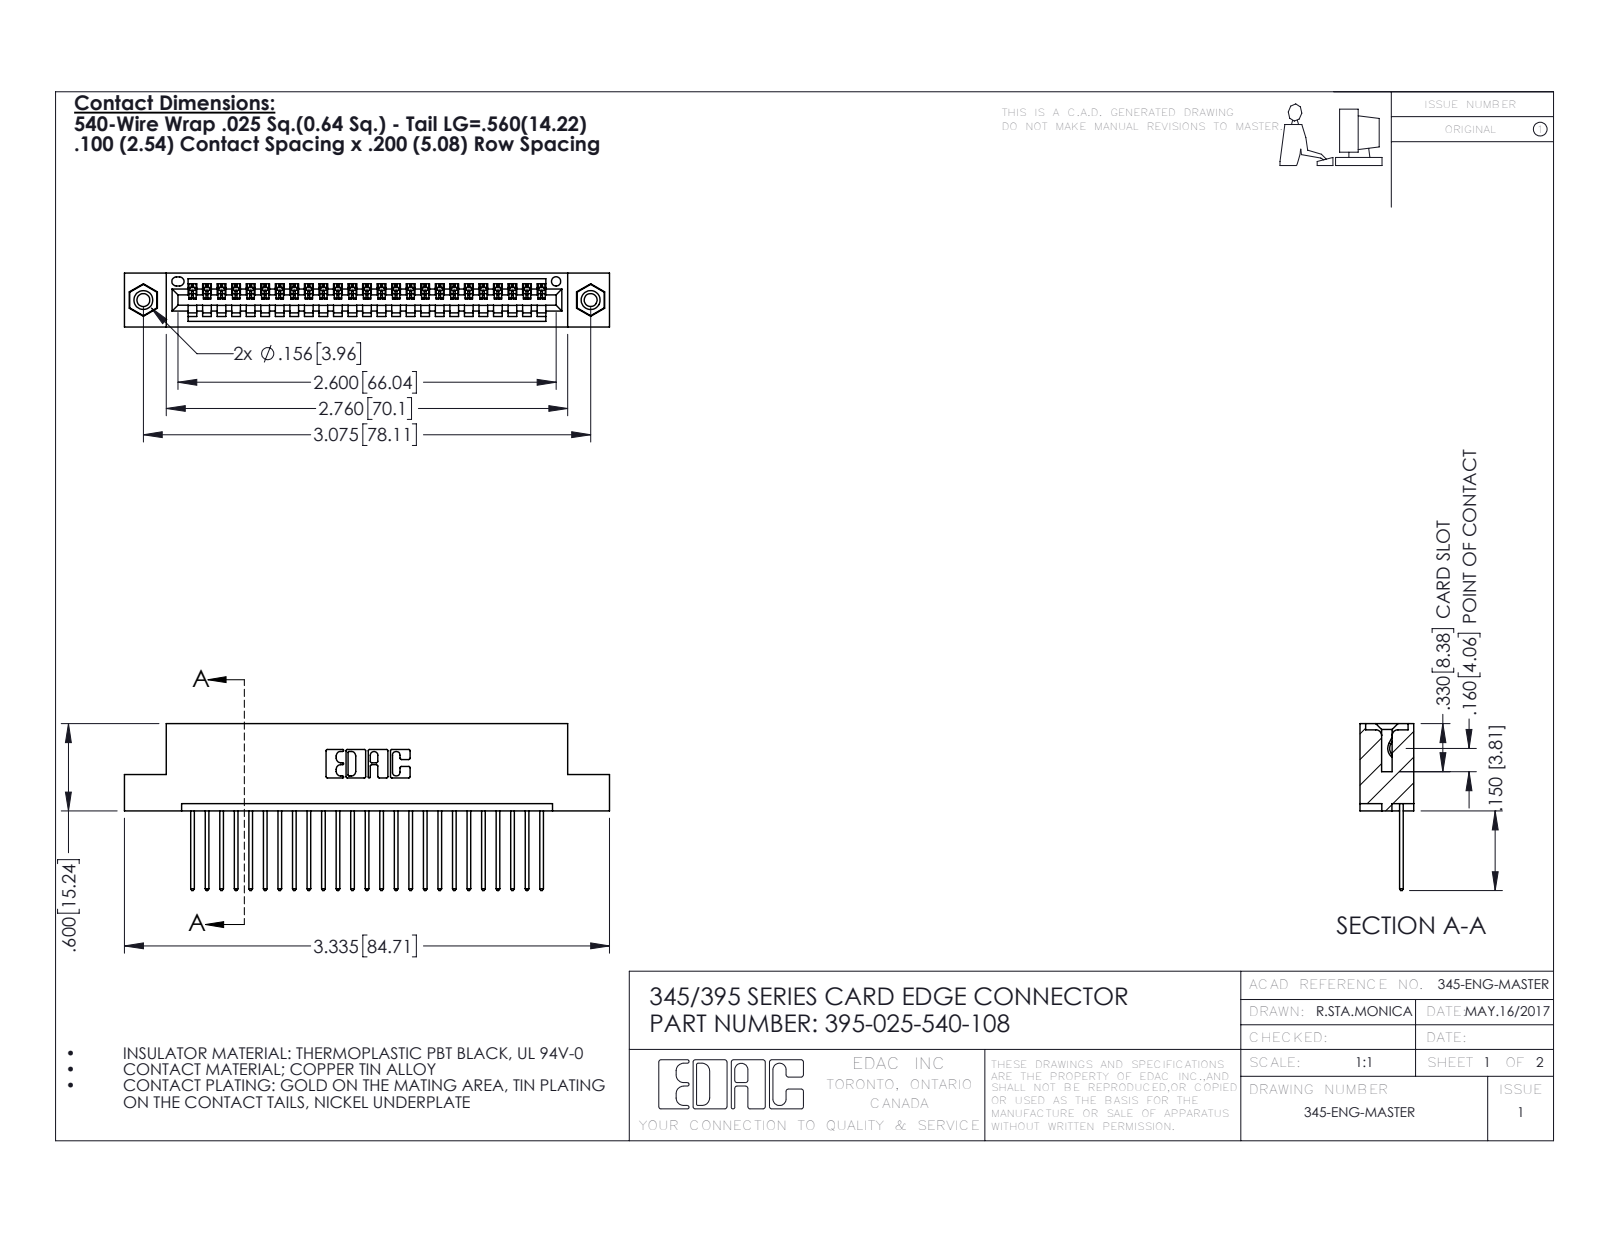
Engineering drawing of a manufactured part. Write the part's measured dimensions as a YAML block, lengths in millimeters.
part_name: "345-250-001_345-250-003-102; 395-025-540-108; 345 Part_Flush Mounting Lugs - 0.156 Dia-TI; 345-292-001_345-293-140"
step_written_by: "SolidWorks 2016 (CONFIG_CONTROL_DESIGN)"
units: millimeters
bodies: {solids: 28, faces: 1636, planar: 1112, cylindrical: 508, other: 16}
overall_size: [84.7, 29.1, 9.4]
volume: 7930
surface_area: 10570
round_holes:
  - {diameter: 2.3, count: 2}
  - {diameter: 3.2, count: 2}
  - {diameter: 4, count: 2}
  - {diameter: 1.6, count: 1}
round_bosses_or_shafts:
  - {diameter: 3.9, count: 2}
partial_cylinders:
  - {radius: 0.2, count: 50}
  - {radius: 0.3, count: 50}
  - {radius: 0.3, count: 22}
  - {radius: 0.2, count: 6}
  - {radius: 0.8, count: 6}
  - {radius: 0.7, count: 3}
  - {radius: 0.8, count: 2}
  - {radius: 1, count: 2}
face_to_face_distances: [1.8, 7.6, 5.1, 9.4, 2.5, 6.9, 0.6, 5.7, 3.8, 1.8]
hole_center_spacings: [6.9, 72.1, 78.1]
